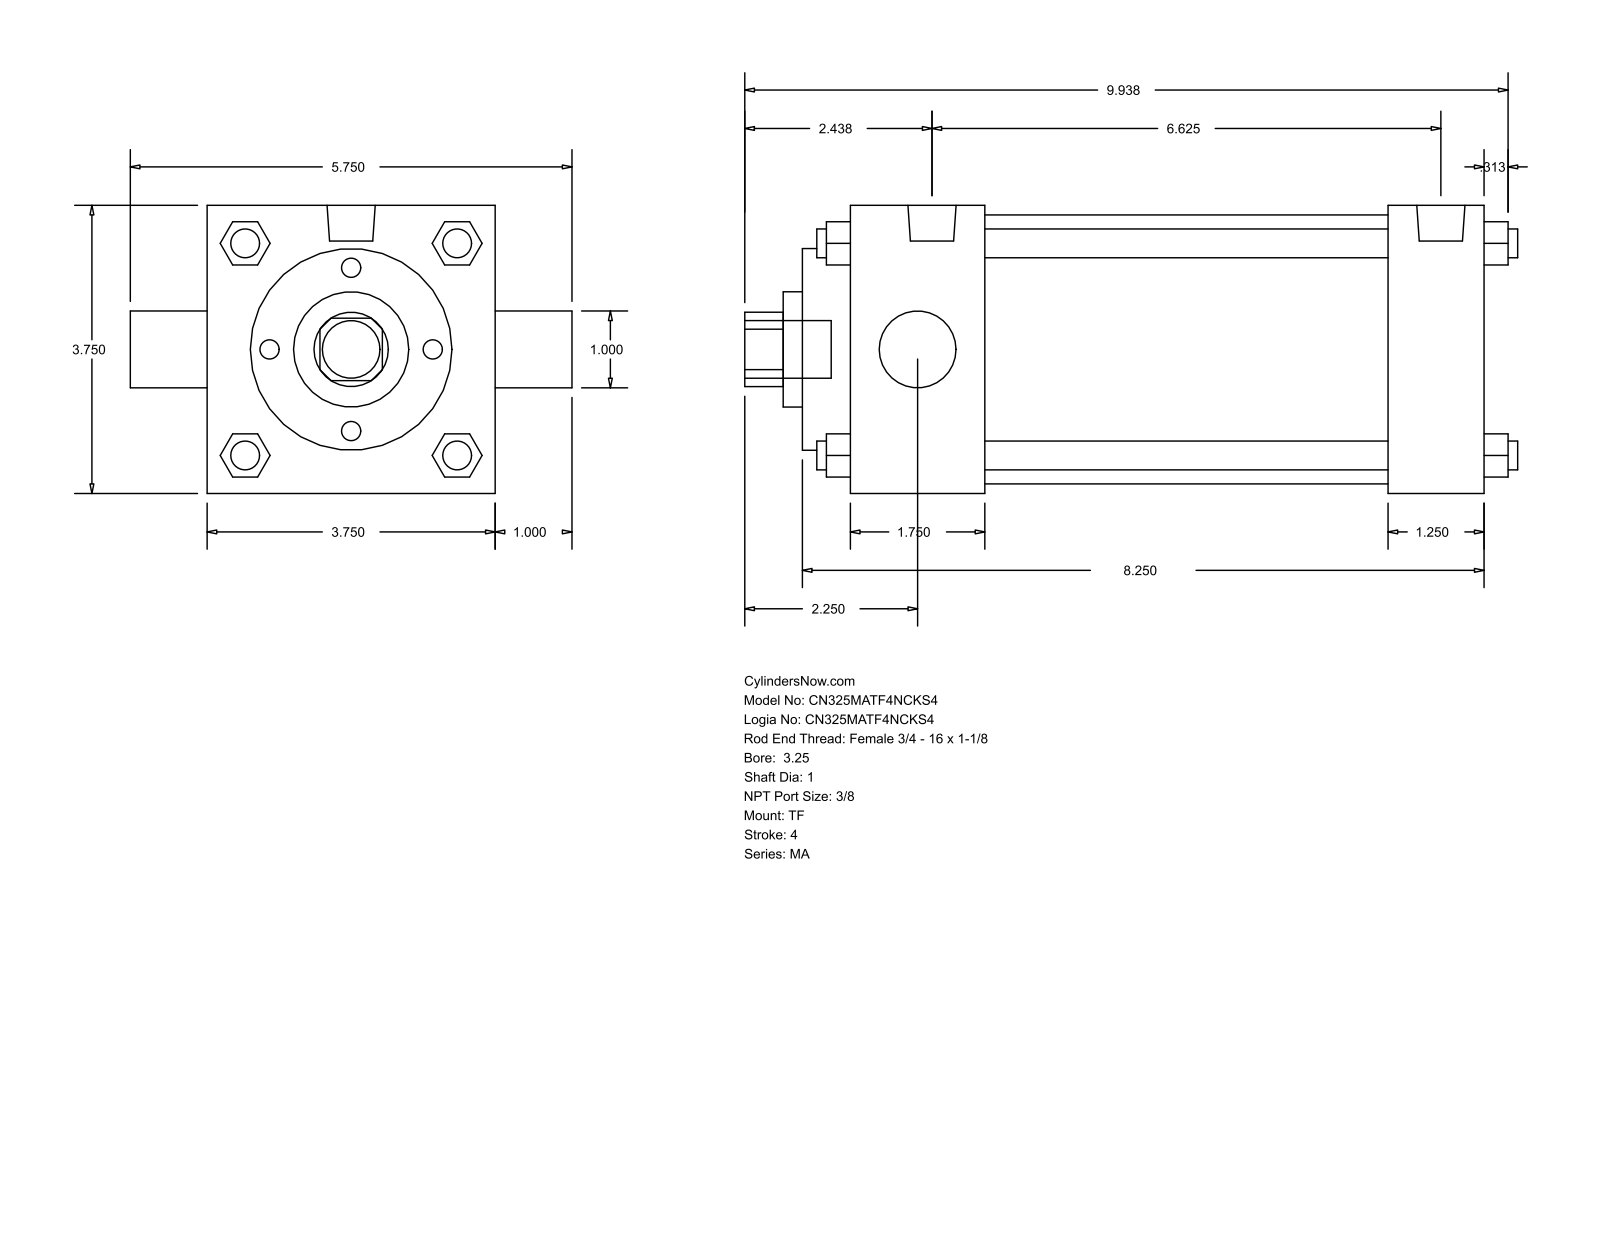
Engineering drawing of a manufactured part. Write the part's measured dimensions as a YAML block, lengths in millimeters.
part_name: "MA_TF__0325_1"
step_written_by: "GSSL Pune (CONFIG_CONTROL_DESIGN)"
units: millimeters
bodies: {solids: 0, faces: 122, planar: 93, cylindrical: 29, other: 0}
overall_size: [255.59, 146.05, 95.25]
round_holes:
  - {diameter: 25.4, count: 2}
  - {diameter: 38.1, count: 1}
  - {diameter: 66.67, count: 1}
  - {diameter: 88.9, count: 1}
round_bosses_or_shafts:
  - {diameter: 9.53, count: 4}
  - {diameter: 11.11, count: 3}
  - {diameter: 15.93, count: 2}
  - {diameter: 19.05, count: 1}
partial_cylinders:
  - {radius: 12.29, count: 1}
face_to_face_distances: [95.24, 209.55, 225.42, 15.87, 44.46, 177.8, 133.34, 165.09, 31.75, 60.33]
